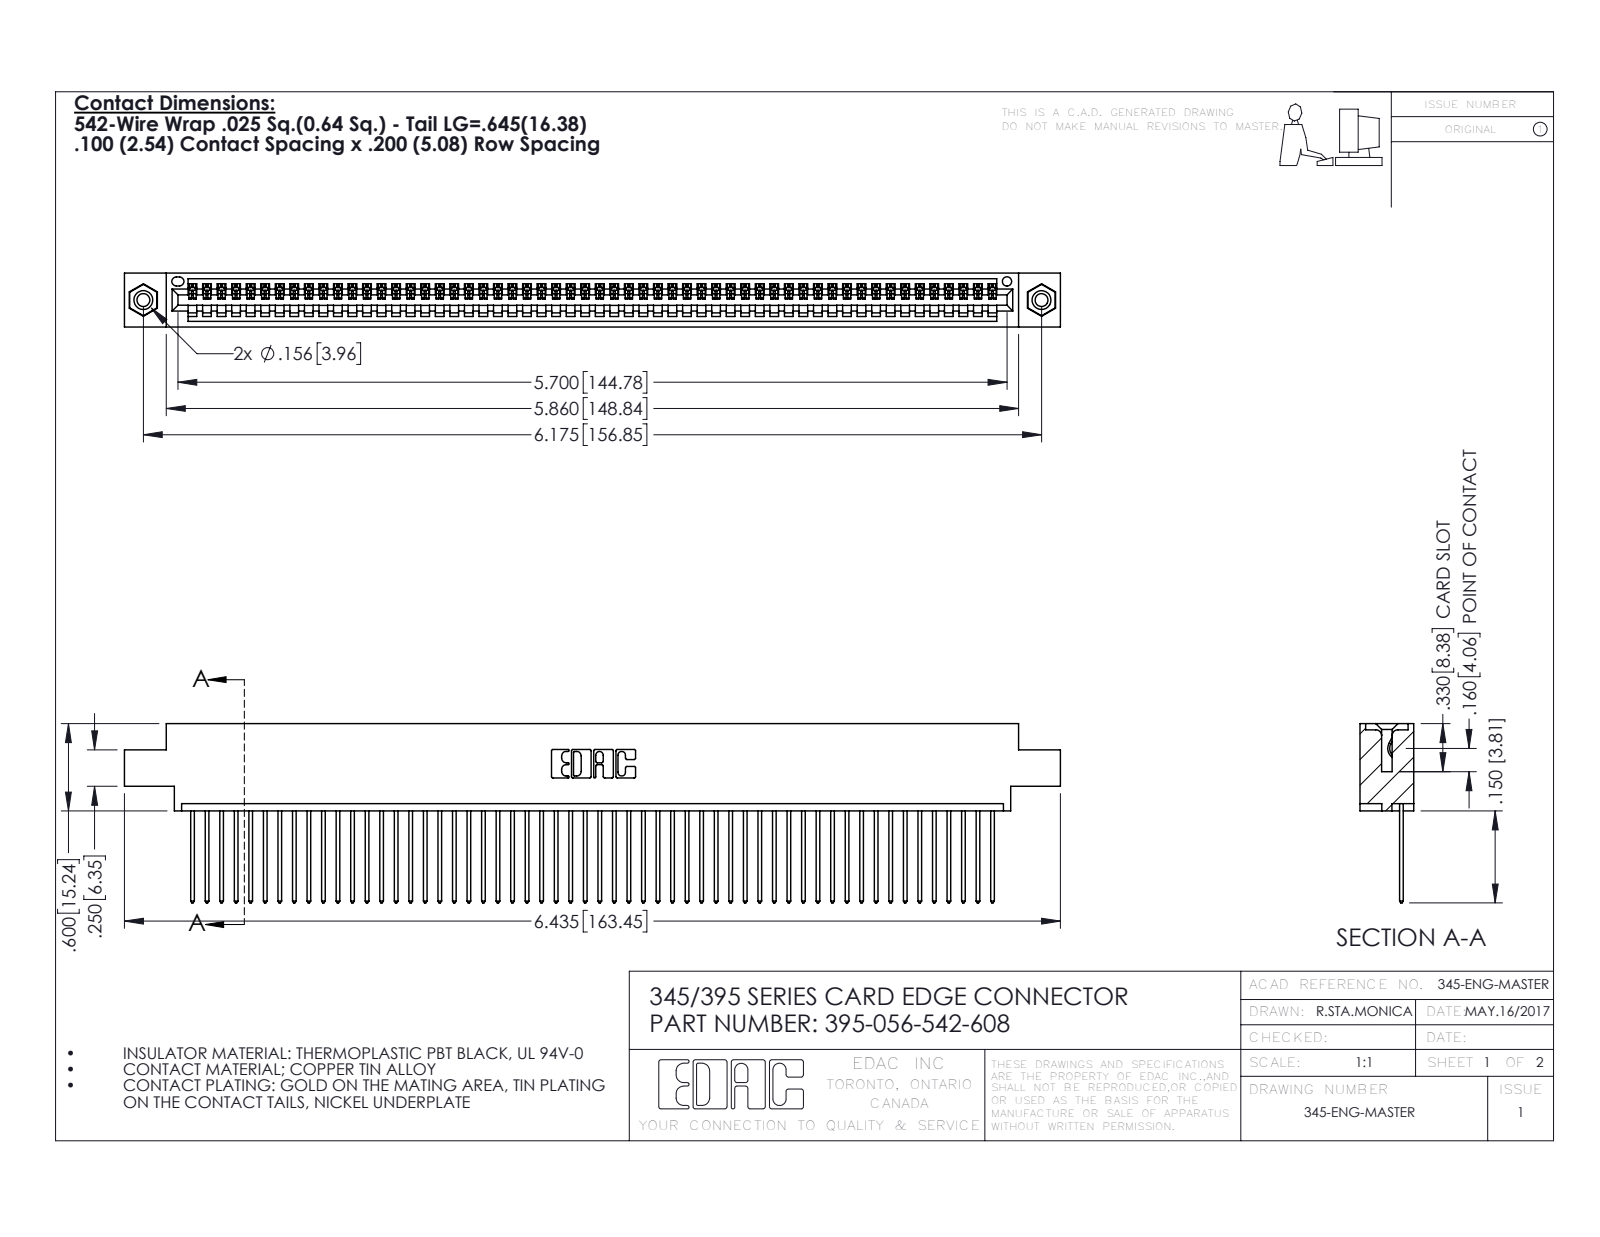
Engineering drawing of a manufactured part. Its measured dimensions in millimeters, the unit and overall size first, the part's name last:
Units: millimetres
Overall size (bounding box): 163.4 × 31.3 × 9.4
Round holes (diameter × count): ⌀2.3 ×2, ⌀3.2 ×2, ⌀4 ×2, ⌀1.6 ×1
Round bosses / shafts (diameter × count): ⌀3.9 ×2
Partial cylindrical surfaces — rounded edges, fillets, slot ends (radius × count): R0.2 ×112, R0.3 ×112, R0.3 ×22, R0.2 ×6, R0.8 ×6, R0.7 ×3, R0.8 ×2, R1 ×2
Main face-to-face distances: 1.8, 7.6, 9.4, 2.5, 6.9, 0.6, 5.1, 5.7, 4.4, 3.8
Hole centre spacings: 6.9, 150.9, 156.8
Volume: 15 600 mm³ · Surface area: 21 920 mm²
Bodies: 59 solids, 3438 faces (2356 planar, 1066 cylindrical, 16 other)
Part name (STEP PRODUCT): 345-250-001_345-250-003-102; 395-056-542-608; 345 Part_0.170 Offset - 0.156 Dia-TI; 345-292-001_345-293-142
STEP written by: SolidWorks 2016 (CONFIG_CONTROL_DESIGN)
